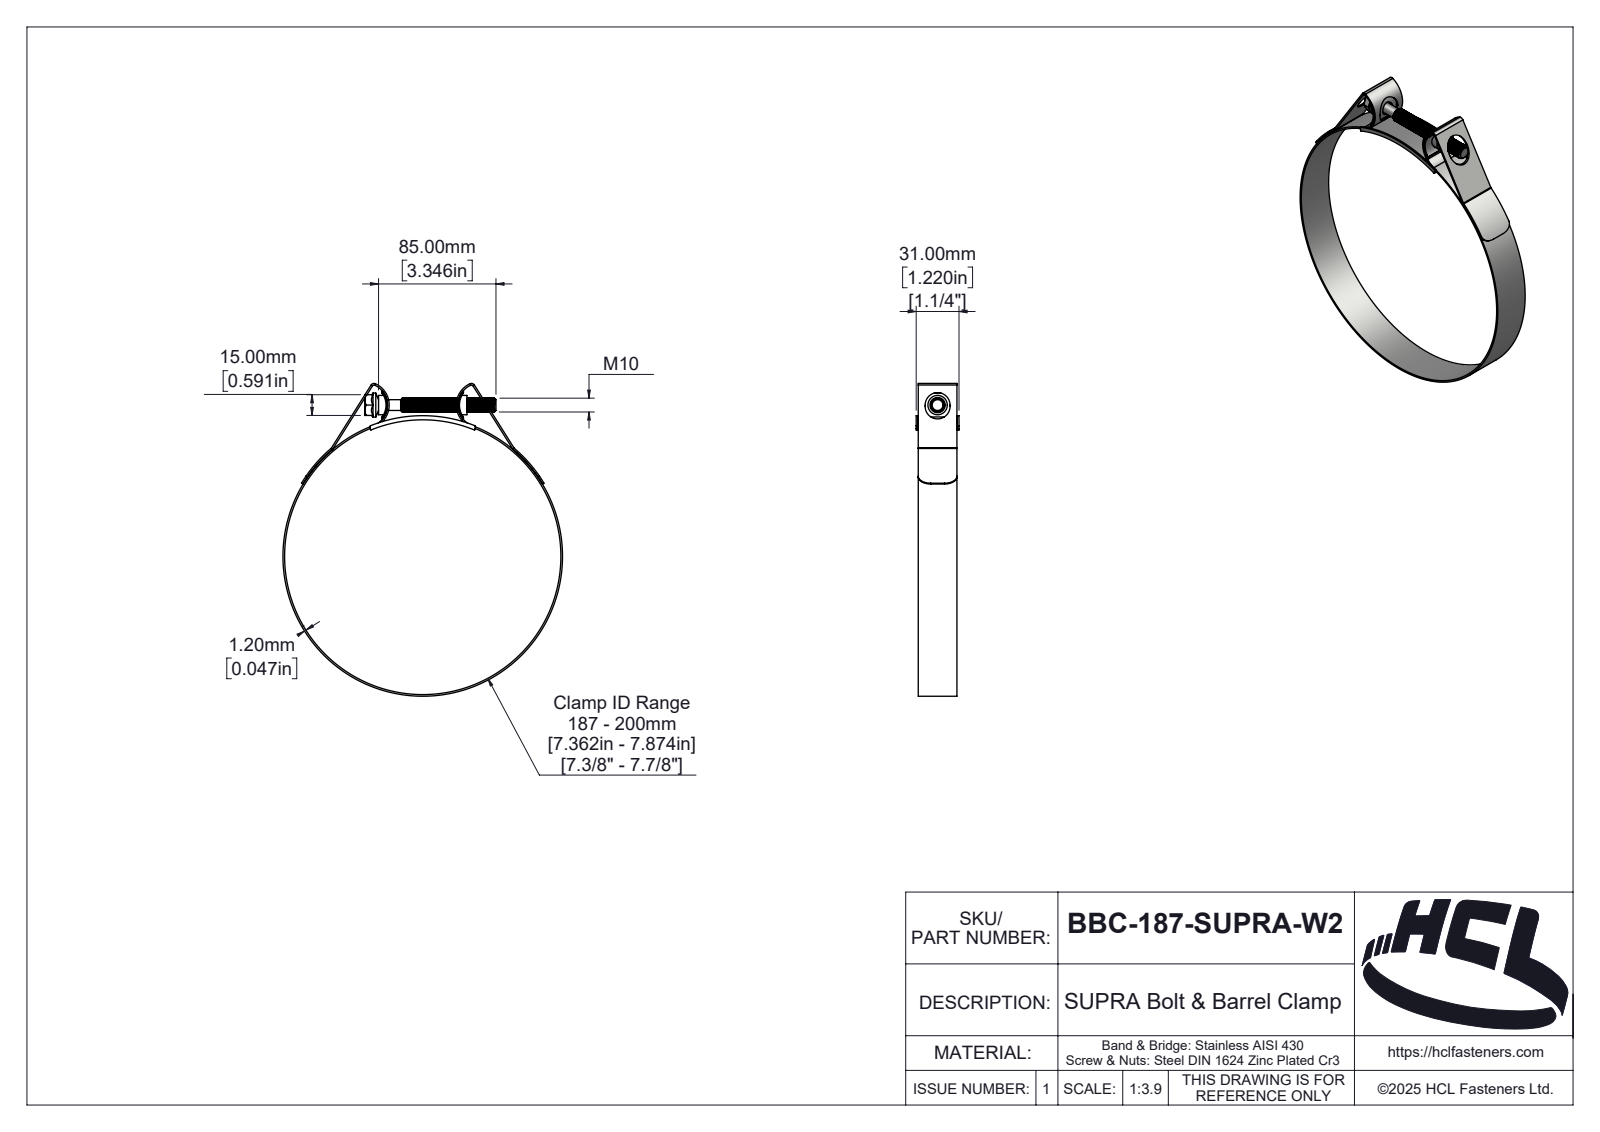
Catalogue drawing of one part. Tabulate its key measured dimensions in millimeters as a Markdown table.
| quantity | value |
| --- | --- |
| part name | BBC-187-SUPRA-W2 |
| STEP written by | SolidWorks 2025 (AUTOMOTIVE_DESIGN) |
| units | millimeters |
| bodies | 5 solids, 384 faces (50 planar, 247 cylindrical, 87 other) |
| overall size | 226.34 × 202.4 × 31 |
| volume | 38 424 mm³ |
| surface area | 58 776 mm² |
| round holes (diameter × count) | 200 × 1 |
| round bosses / shafts (diameter × count) | 202.4 × 1, 17.32 × 1, 14 × 1, 10 × 1, 7.8 × 1 |
| partial cylindrical surfaces (radius × count) | 1 × 4, 1.3 × 2, 2 × 2, 2.5 × 2, 3.2 × 2, 9 × 2, 14.68 × 2, 15.68 × 2 |
| main face-to-face distances | 1.2, 28, 1.5, 29.5, 29.8, 28.3, 31, 28.6, 15, 2.5 |
